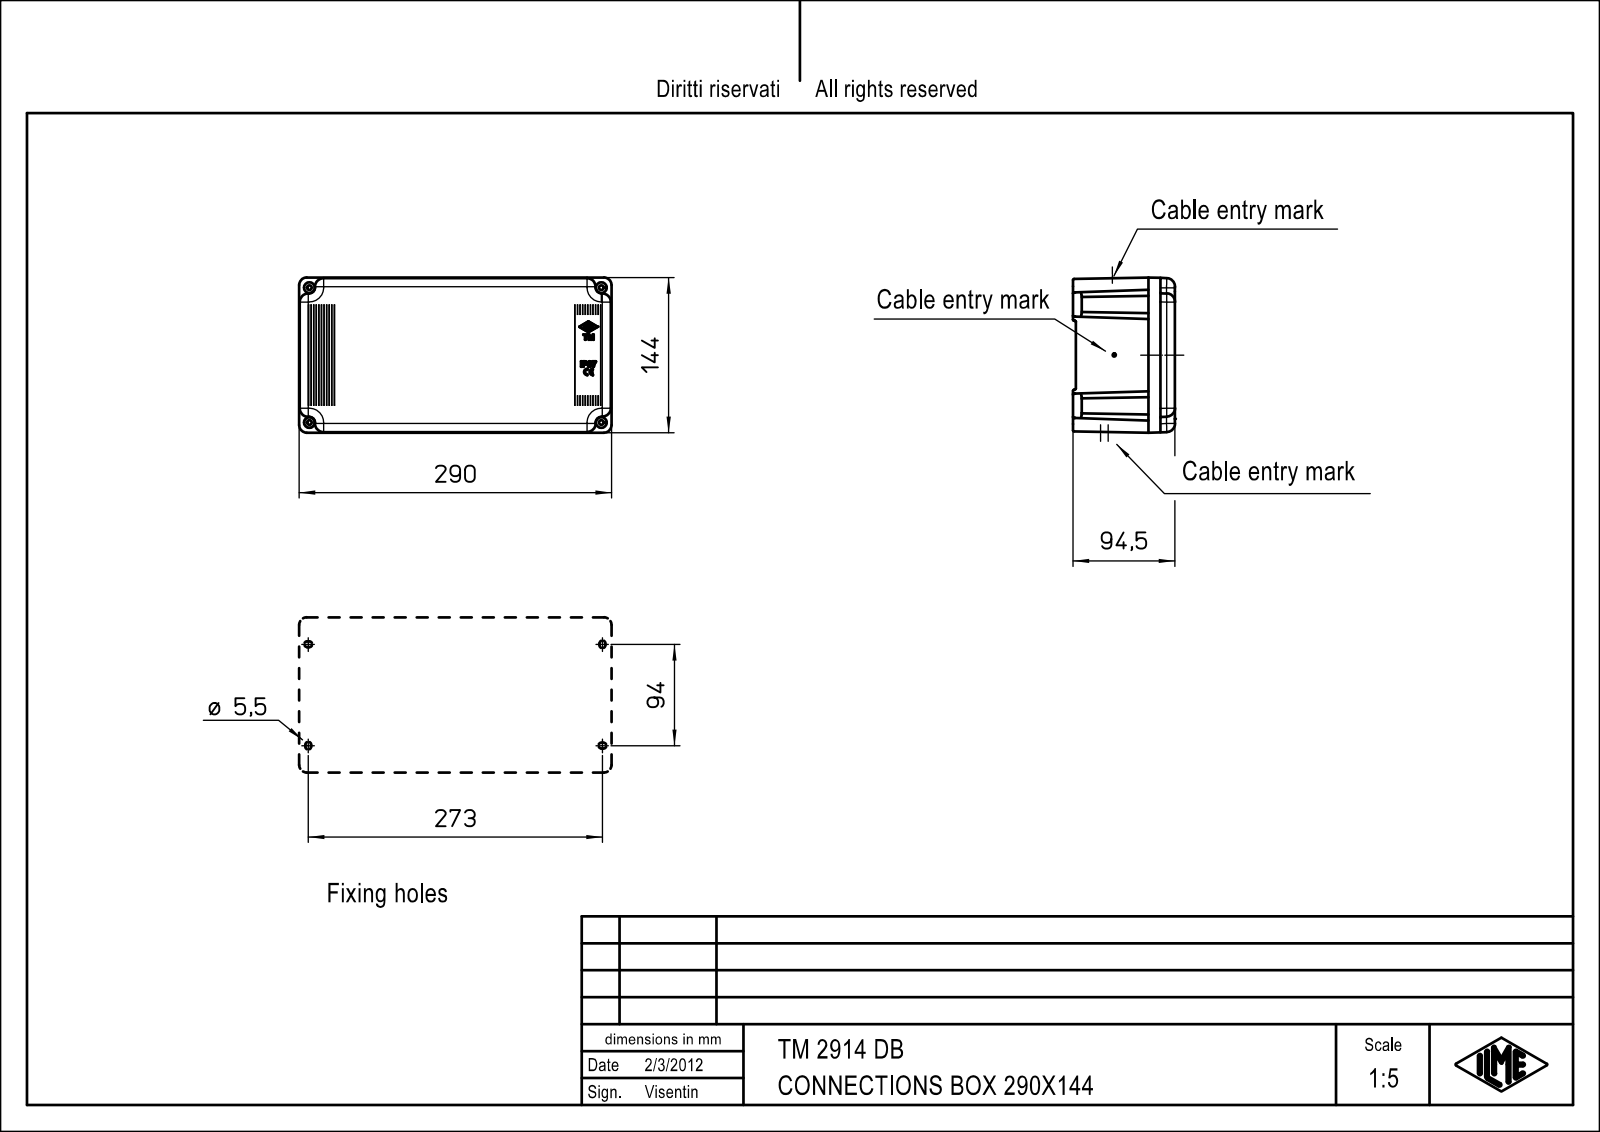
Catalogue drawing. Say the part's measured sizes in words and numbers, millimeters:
The part is named "SCATOLA_2914; COPERCHIO_2914; TM_2914_DB". Its 3-D file was written by "Creo Elements/Direct Modeling 20.5B 27-May-2023 (C) Parametric Technology GmbH (AUTOMOTIVE_DESIGN)". It is 2 solids with 1153 faces: 824 planar, 243 cylindrical and 86 other. Overall it measures 290 by 144 by 94.9 millimeters. Its volume is 857 582 cubic millimeters and its surface area 325 234 square millimeters. Round holes: 4 of diameter 5.2. Round bosses or shafts: 4 of diameter 8.5, 4 of diameter 5. Partial cylindrical surfaces (rounded edges, fillets, slot ends): 124 of radius 0.2, 16 of radius 8, 11 of radius 0.25, 8 of radius 2.7, 8 of radius 3, 8 of radius 3.5, 8 of radius 7, 8 of radius 9.5. The main face-to-face distances are 87, 5, 92, 82, 5.37, 62.5, 24.5, 67.5, 19.5, 7. The hole center spacings are 125, 271, 298.44.
